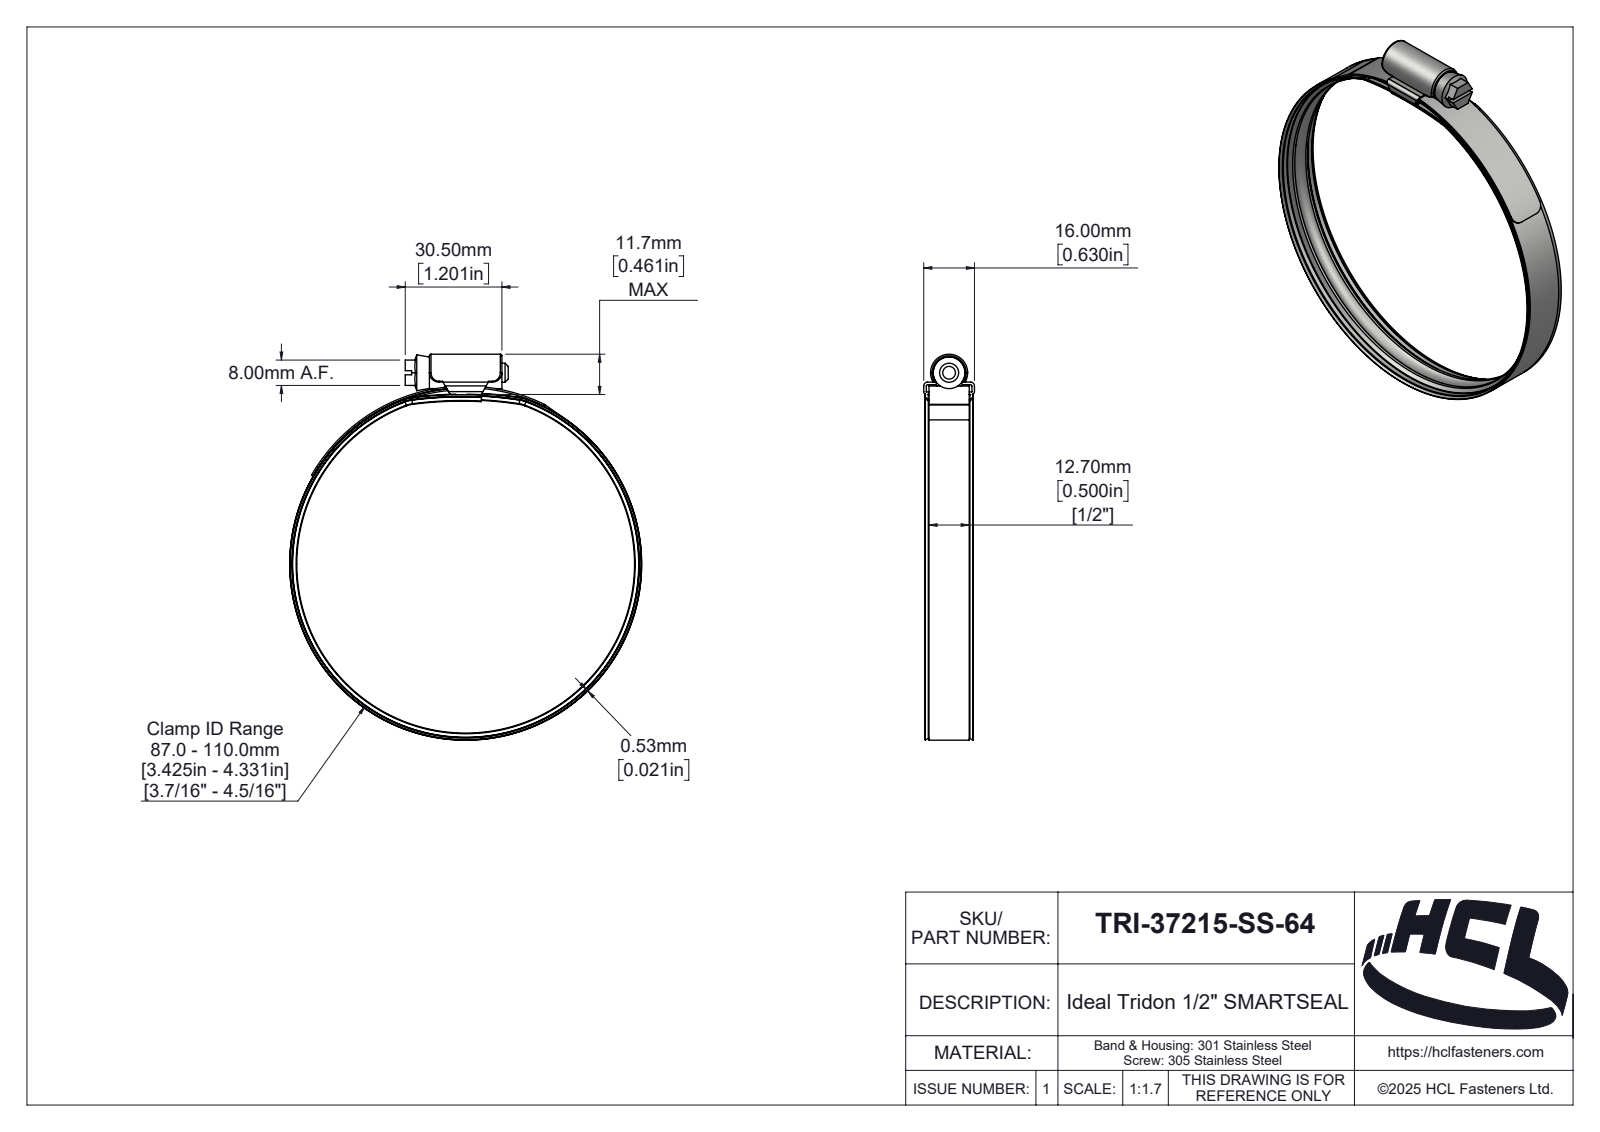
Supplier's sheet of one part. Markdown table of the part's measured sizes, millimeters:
| quantity | value |
| --- | --- |
| part name | TRI-37215-SS-64 |
| STEP written by | SolidWorks 2025 (AUTOMOTIVE_DESIGN) |
| units | millimeters |
| bodies | 4 solids, 418 faces (42 planar, 119 cylindrical, 257 other) |
| overall size | 121.73 × 111.06 × 16 |
| volume | 6 978 mm³ |
| surface area | 25 751 mm² |
| round holes (diameter × count) | 109.4 × 1, 110 × 1 |
| round bosses / shafts (diameter × count) | 111.06 × 1, 109.8 × 1, 10 × 1, 6 × 1 |
| partial cylindrical surfaces (radius × count) | 0.5 × 6, 3 × 4, 0.1 × 2, 0.9 × 2, 1.2 × 2, 9.9 × 2, 10.1 × 2, 0.46 × 1 |
| main face-to-face distances | 0.8, 12.7, 3.1, 0.53, 2.3, 30.5, 3.9, 1.65, 14.35, 15.2 |
